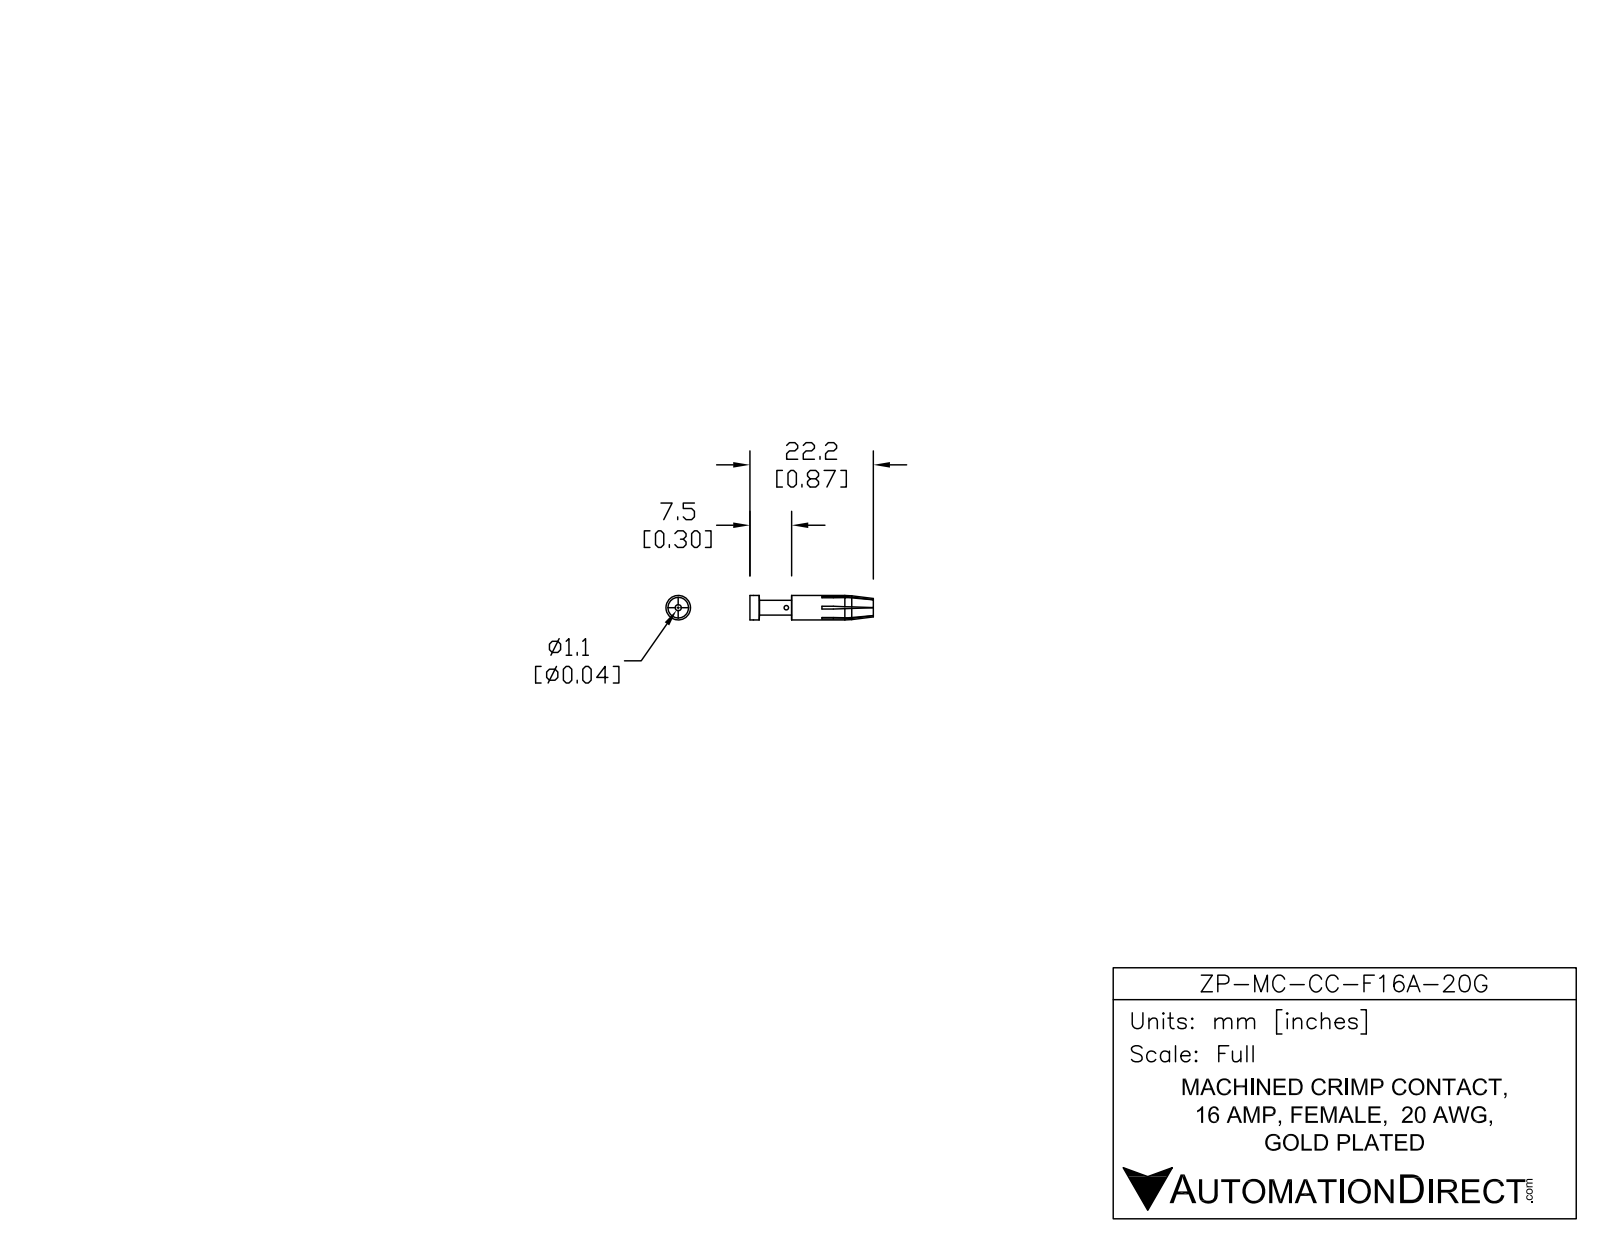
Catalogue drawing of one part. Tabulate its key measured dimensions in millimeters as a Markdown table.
| quantity | value |
| --- | --- |
| part name | ZP-MC-CC-F16A-20G |
| STEP written by | SolidWorks 2014 (AUTOMOTIVE_DESIGN) |
| units | millimeters |
| bodies | 1 solid, 75 faces (39 planar, 10 cylindrical, 26 other) |
| overall size | 22.2 × 4.42 × 4.42 |
| volume | 190 mm³ |
| surface area | 485 mm² |
| round holes (diameter × count) | 0.8 × 1, 1.1 × 1 |
| round bosses / shafts (diameter × count) | 4.42 × 1, 2.63 × 1 |
| main face-to-face distances | 0.5, 14.7, 22.2, 7.5, 9.25, 5.45, 12.95, 14.2, 4.95, 8 |
